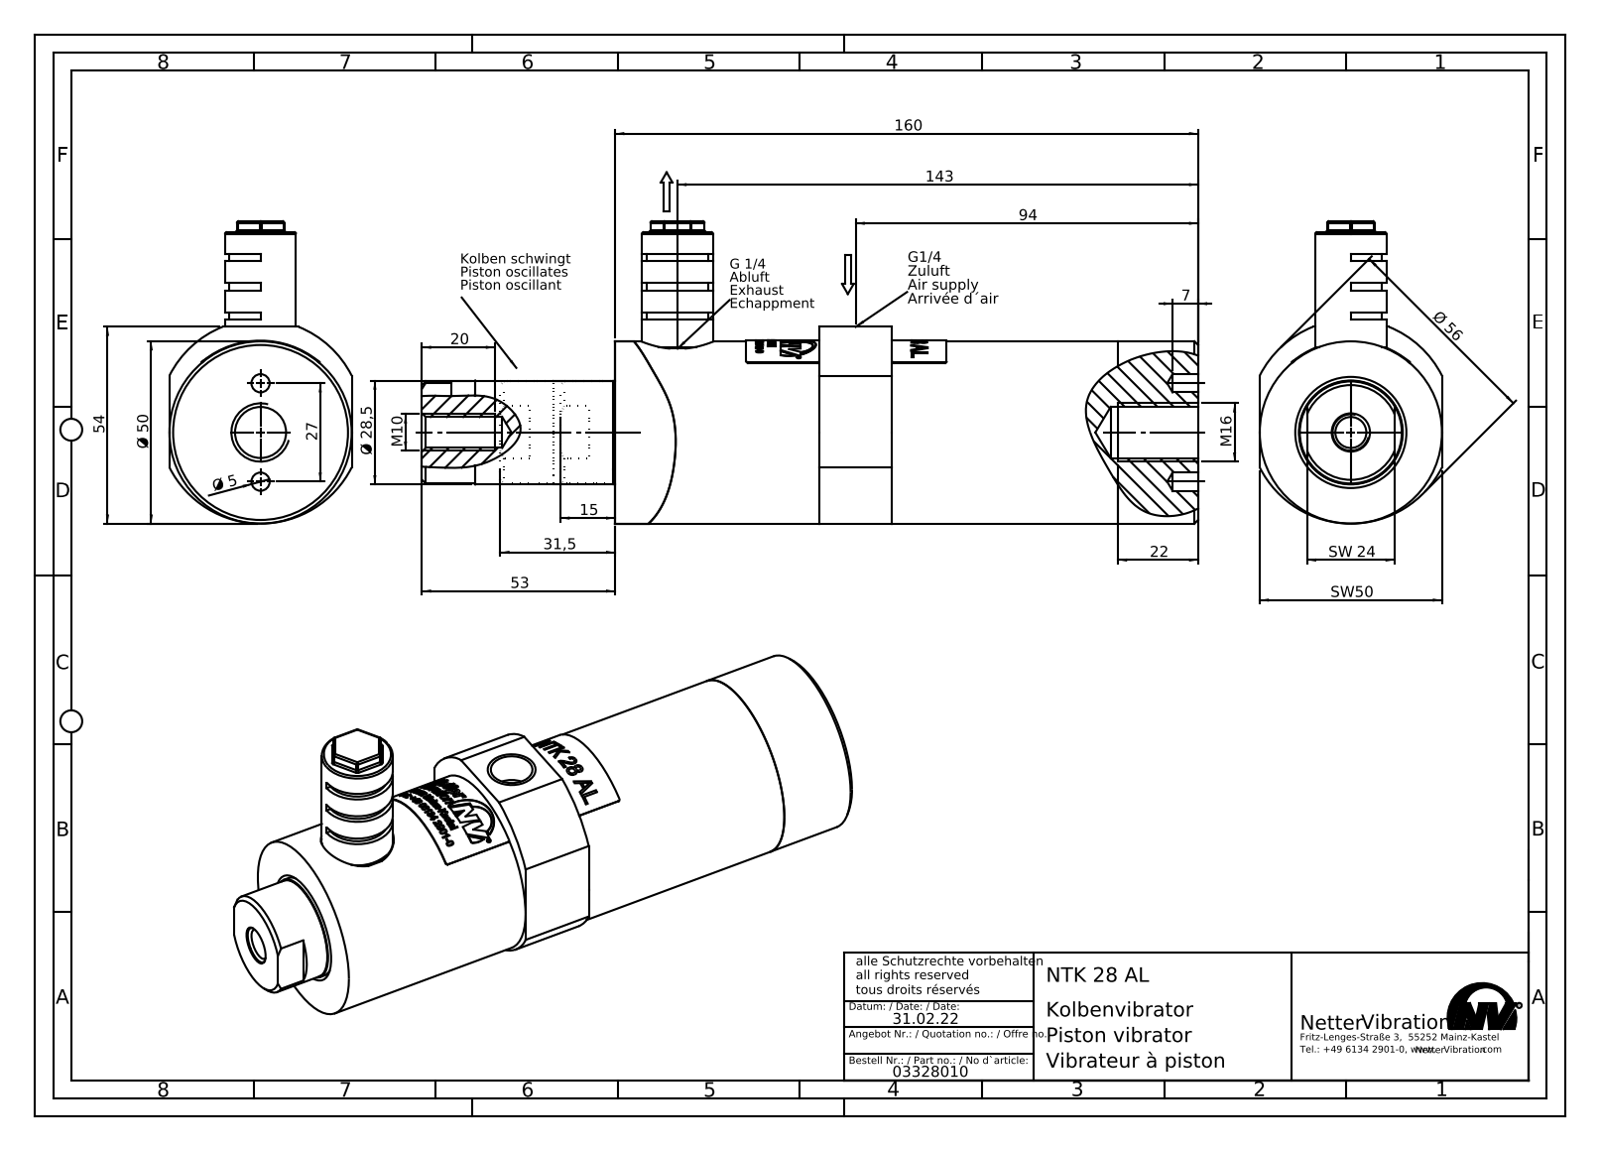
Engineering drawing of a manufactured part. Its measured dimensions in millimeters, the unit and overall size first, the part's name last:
Units: millimetres
Overall size (bounding box): 175 × 85 × 50
Round holes (diameter × count): ⌀5 ×2, ⌀11.45 ×2, ⌀4 ×1, ⌀8.5 ×1, ⌀14 ×1, ⌀20 ×1, ⌀25 ×1, ⌀37 ×1
Round bosses / shafts (diameter × count): ⌀50 ×1, ⌀36.9 ×1, ⌀28.5 ×1, ⌀28 ×1, ⌀19.5 ×1, ⌀13.16 ×1
Partial cylindrical surfaces — rounded edges, fillets, slot ends (radius × count): R0.5 ×22, R8.5 ×1, R25.2 ×1, R28 ×1
Main face-to-face distances: 22, 138, 160, 17, 121, 39, 8, 56, 26, 18
Hole centre spacings: 13.5, 27, 48.9
Volume: 344 476 mm³ · Surface area: 65 596 mm²
Bodies: 5 solids, 175 faces (49 planar, 80 cylindrical, 46 other)
Part name (STEP PRODUCT): NTK 28 AL #03328010
STEP written by: SolidWorks 2015 (AUTOMOTIVE_DESIGN)
